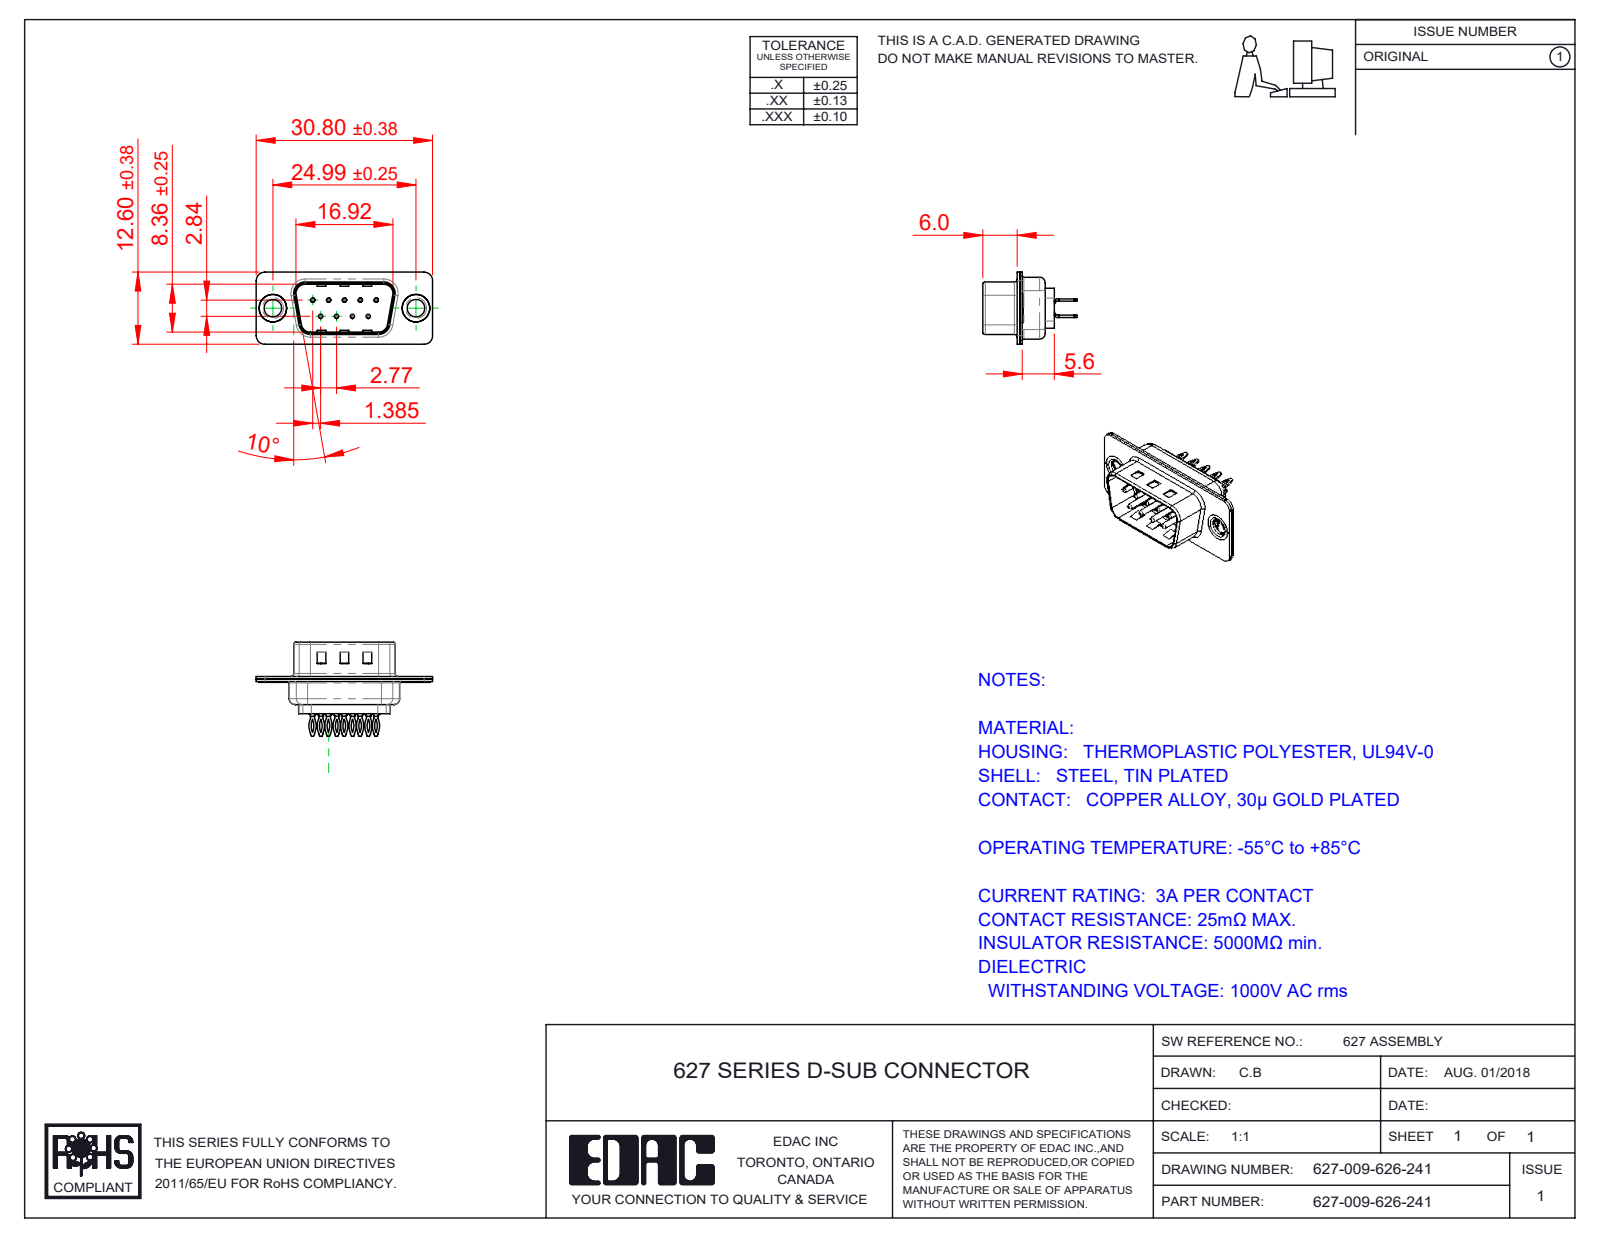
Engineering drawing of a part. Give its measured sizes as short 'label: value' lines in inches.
name: 627 Shell Front_09 Contacts; 627 Contact Row 1_26L; 627 Contact Row 2_26L; 627 Shell Rear_09 Contacts (+3 more)
written by: SolidWorks 2020 (CONFIG_CONTROL_DESIGN)
unit: in
bodies: 14 solids, 962 faces (287 planar, 392 cylindrical, 283 other)
size: 1.213 × 0.648 × 0.496
volume: 0.075 in³; area: 5.83 in²
holes: 9× ⌀0.014, 9× ⌀0.043, 9× ⌀0.063, 2× ⌀0.12, 2× ⌀0.157, 2× ⌀0.189
bosses: 9× ⌀0.079, 9× ⌀0.059, 9× ⌀0.03, 2× ⌀0.197, 2× ⌀0.193, 2× ⌀0.14
rounds: 18× R0.059, 18× R0.115, 18× R0.131, 12× R0.079, 8× R0.02, 8× R0.063, 4× R0.01, 4× R0.024
face distances: 0.016, 0.018, 0.035, 0.032, 0.377, 0.055, 0.02, 0.345, 0.059, 0.238
hole spacings: 0.124, 0.109, 0.218, 0.198, 0.198, 0.327, 0.294, 0.295
